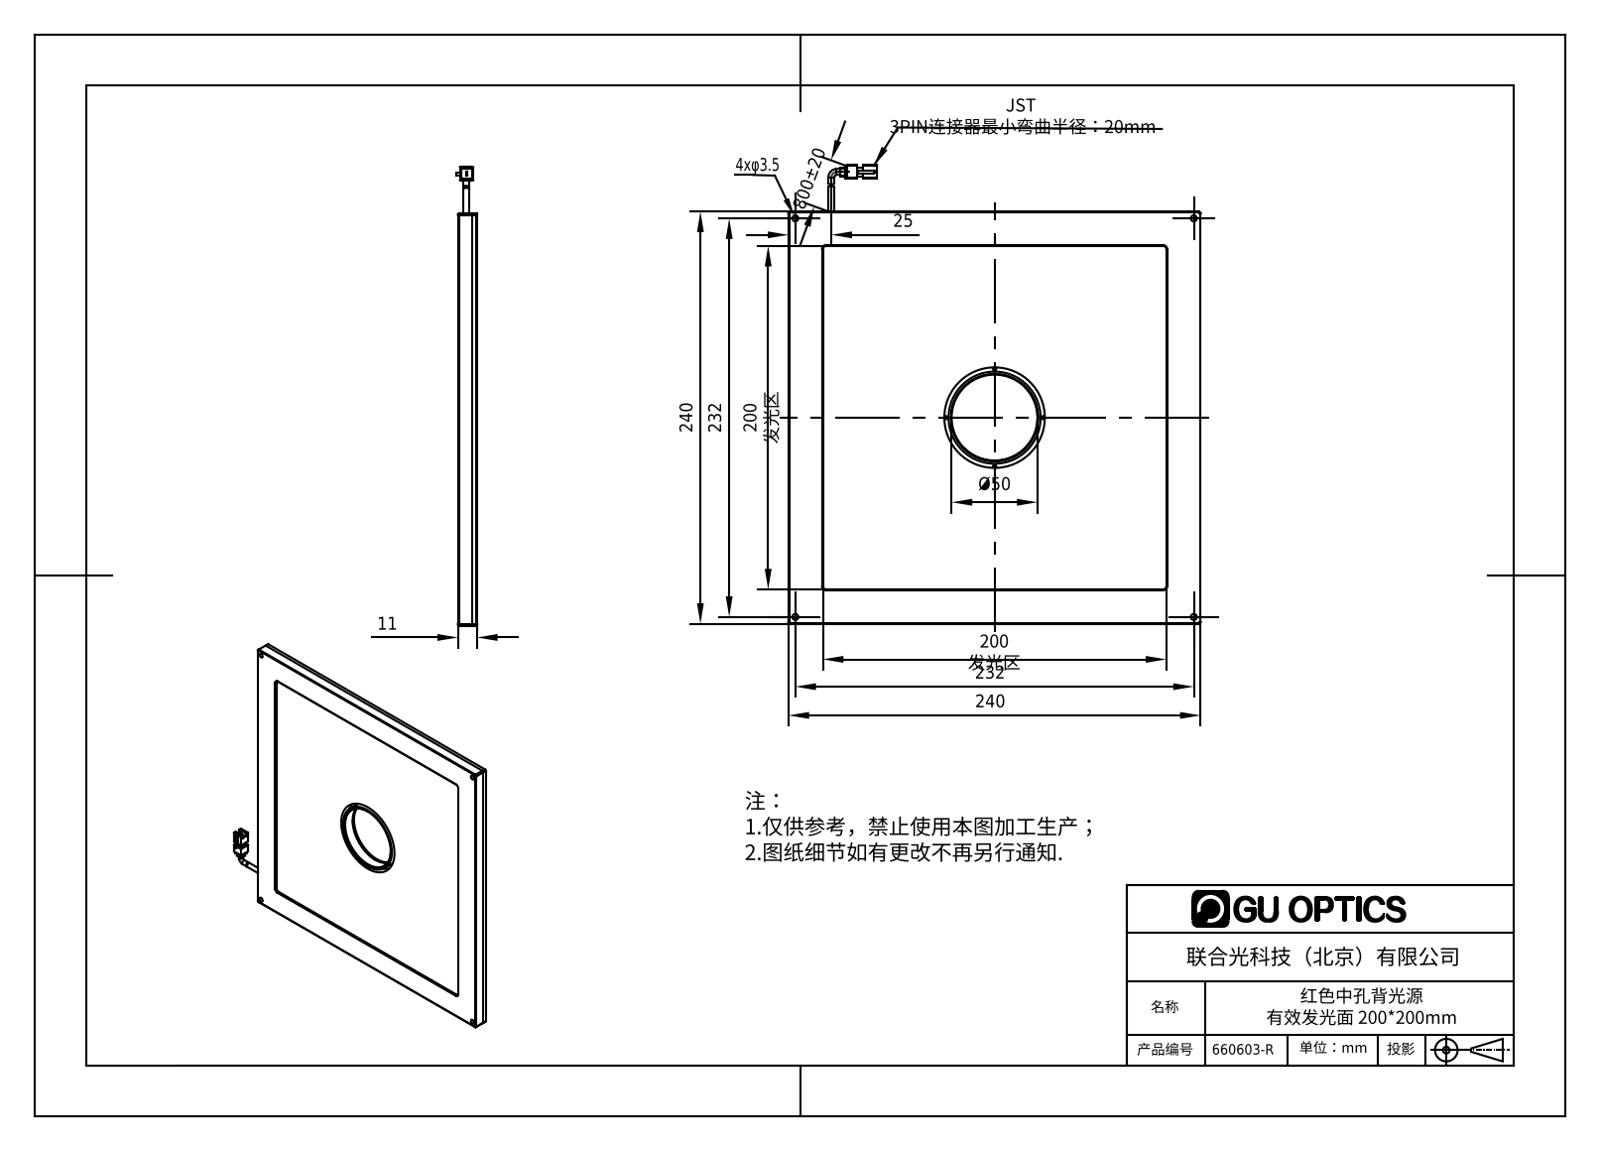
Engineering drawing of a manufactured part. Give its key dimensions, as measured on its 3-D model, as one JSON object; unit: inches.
{"part_name": "660603-R", "step_written_by": "SolidWorks 2016 (AUTOMOTIVE_DESIGN)", "units": "inches", "bodies": {"solids": 6, "faces": 509, "planar": 192, "cylindrical": 170, "other": 147}, "overall_size": [10.512, 9.449, 0.472], "volume_in3": 33.63, "surface_area_in2": 425.6, "round_holes": [[0.079, 20], [0.063, 16], [0.094, 16], [0.138, 4], [1.969, 1], [2.303, 1], [2.441, 1]], "round_bosses_or_shafts": [[0.138, 2], [2.11, 1]], "partial_cylinders_radius": [[0.02, 8], [0.039, 6], [0.059, 4], [0.079, 4], [0.197, 4]], "face_to_face_distances": [0.118, 0.386, 0.268, 0.315, 0.047, 0.433, 0.039, 0.394, 0.276, 0.236], "hole_center_spacings": [0.243, 2.874, 3.111, 3.183, 4.85, 5.787, 6.024, 6.09]}
